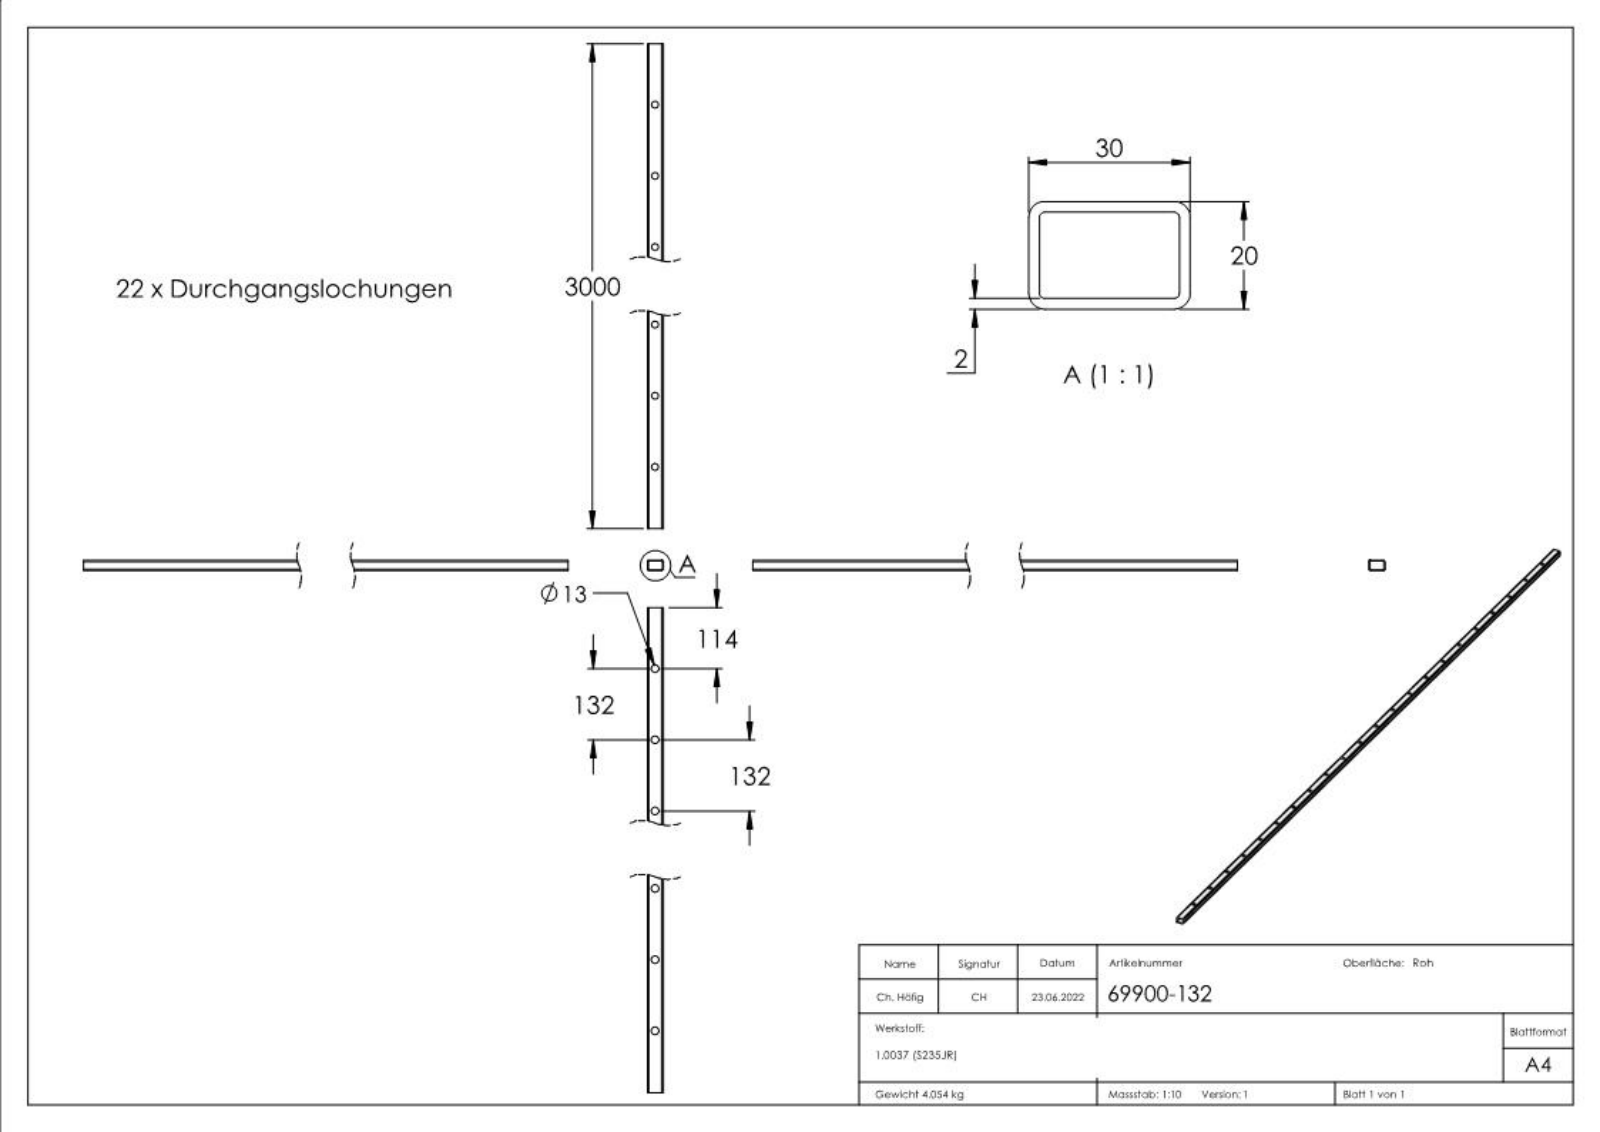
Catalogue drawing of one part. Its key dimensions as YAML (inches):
part_name: "69900-132"
step_written_by: "SolidWorks 2018 (CONFIG_CONTROL_DESIGN)"
units: inches
bodies: {solids: 1, faces: 325, planar: 140, cylindrical: 52, other: 133}
overall_size: [118.11, 1.181, 0.787]
volume: 31.72
surface_area: 811.7
round_holes:
  - {diameter: 0.512, count: 22}
partial_cylinders:
  - {radius: 0.039, count: 4}
  - {radius: 0.118, count: 4}
face_to_face_distances: [0.079, 0.709, 1.102, 0.63, 0.787, 1.181, 1.024, 118.11, 0.075, 1.028]
hole_center_spacings: [5.197, 10.394, 15.591, 20.787, 25.984, 31.181, 36.378, 41.575]
